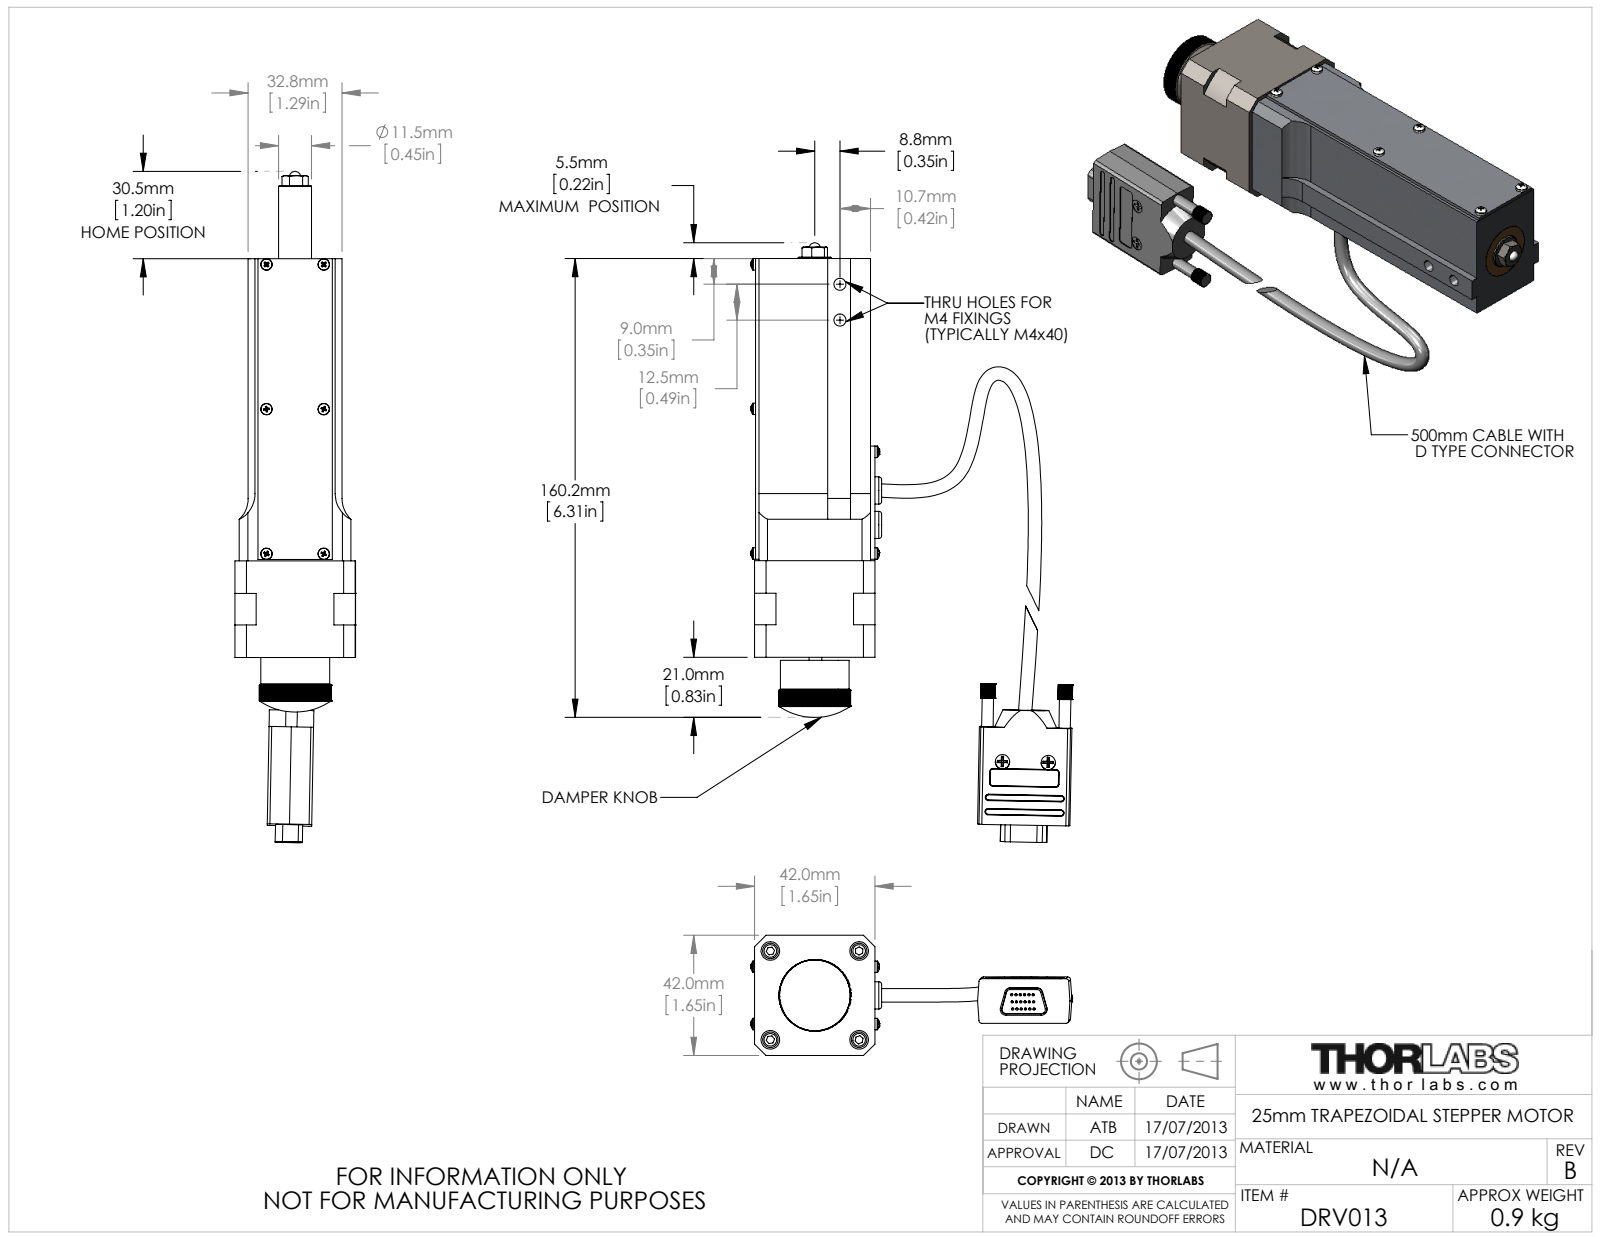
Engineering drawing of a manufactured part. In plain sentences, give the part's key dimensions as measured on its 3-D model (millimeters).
The part is named "DRV013 - Modular 25mm Motor Drive". Its 3-D file was written by "SolidWorks 2011 (AUTOMOTIVE_DESIGN)". It is 0 solids with 1037 faces: 724 planar, 224 cylindrical and 89 other. Overall it measures 173.7 by 45.97 by 42 millimeters. Round holes: 4 of diameter 6.5, 2 of diameter 4.2, 2 of diameter 4.8, 1 of diameter 2.5, 1 of diameter 3.99, 1 of diameter 19. Round bosses or shafts: 8 of diameter 4, 2 of diameter 5.4, 1 of diameter 24, 1 of diameter 12. Partial cylindrical surfaces (rounded edges, fillets, slot ends): 4 of radius 10, 1 of radius 12.5, 1 of radius 25. The main face-to-face distances are 1.5, 42, 40.5, 7, 35, 28, 40.2, 41.7, 39, 33.5. The hole center spacings are 21.92, 31, 43.84, 12, 12.5.
